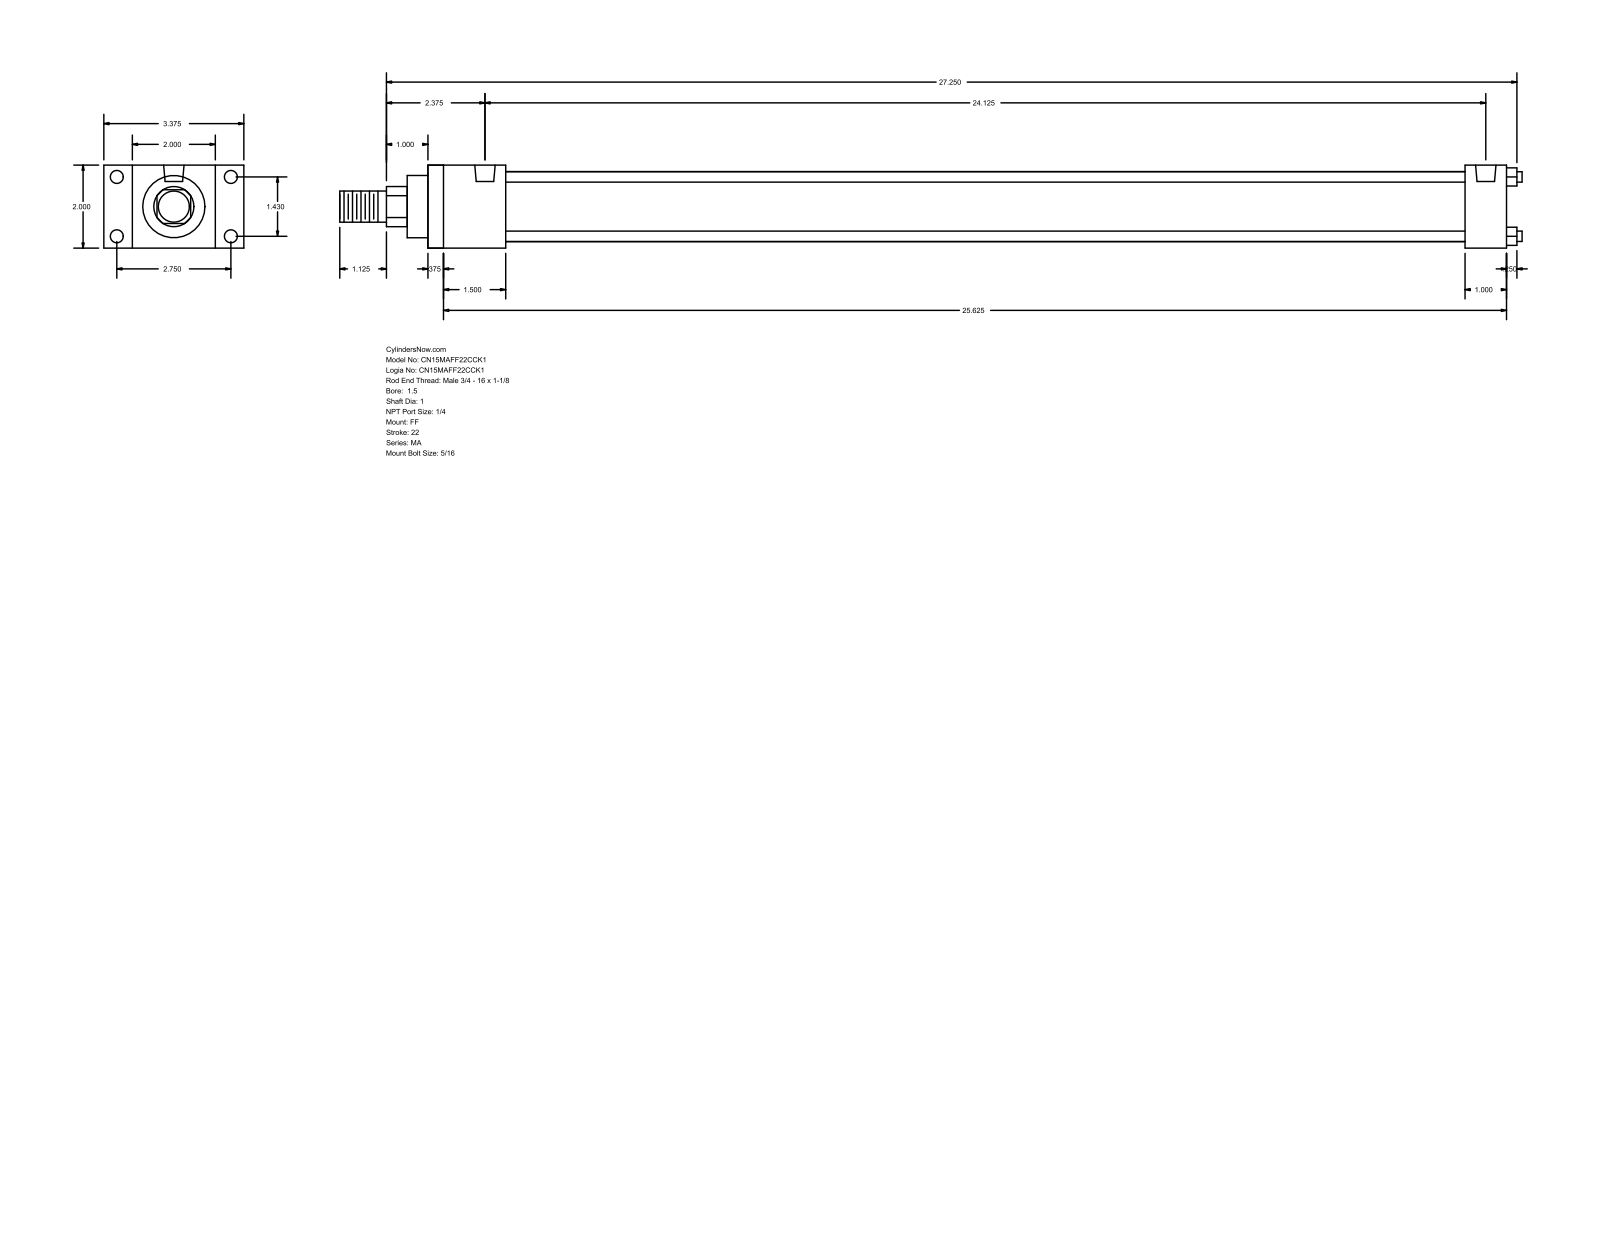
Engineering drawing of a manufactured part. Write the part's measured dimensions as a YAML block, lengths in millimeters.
part_name: "MA_FF__0150_1"
step_written_by: "GSSL Pune (CONFIG_CONTROL_DESIGN)"
units: millimeters
bodies: {solids: 0, faces: 92, planar: 64, cylindrical: 28, other: 0}
overall_size: [723.9, 85.72, 50.8]
round_holes:
  - {diameter: 7.94, count: 8}
  - {diameter: 12.49, count: 2}
round_bosses_or_shafts:
  - {diameter: 6.35, count: 4}
  - {diameter: 42.93, count: 1}
  - {diameter: 38.1, count: 1}
  - {diameter: 25.4, count: 1}
  - {diameter: 19.05, count: 1}
partial_cylinders:
  - {radius: 12.29, count: 1}
face_to_face_distances: [50.8, 660.4, 9.52, 650.88, 25.4, 47.63, 635, 38.11, 625.48, 587.37]
hole_center_spacings: [36.32, 69.84, 78.72, 612.77]
